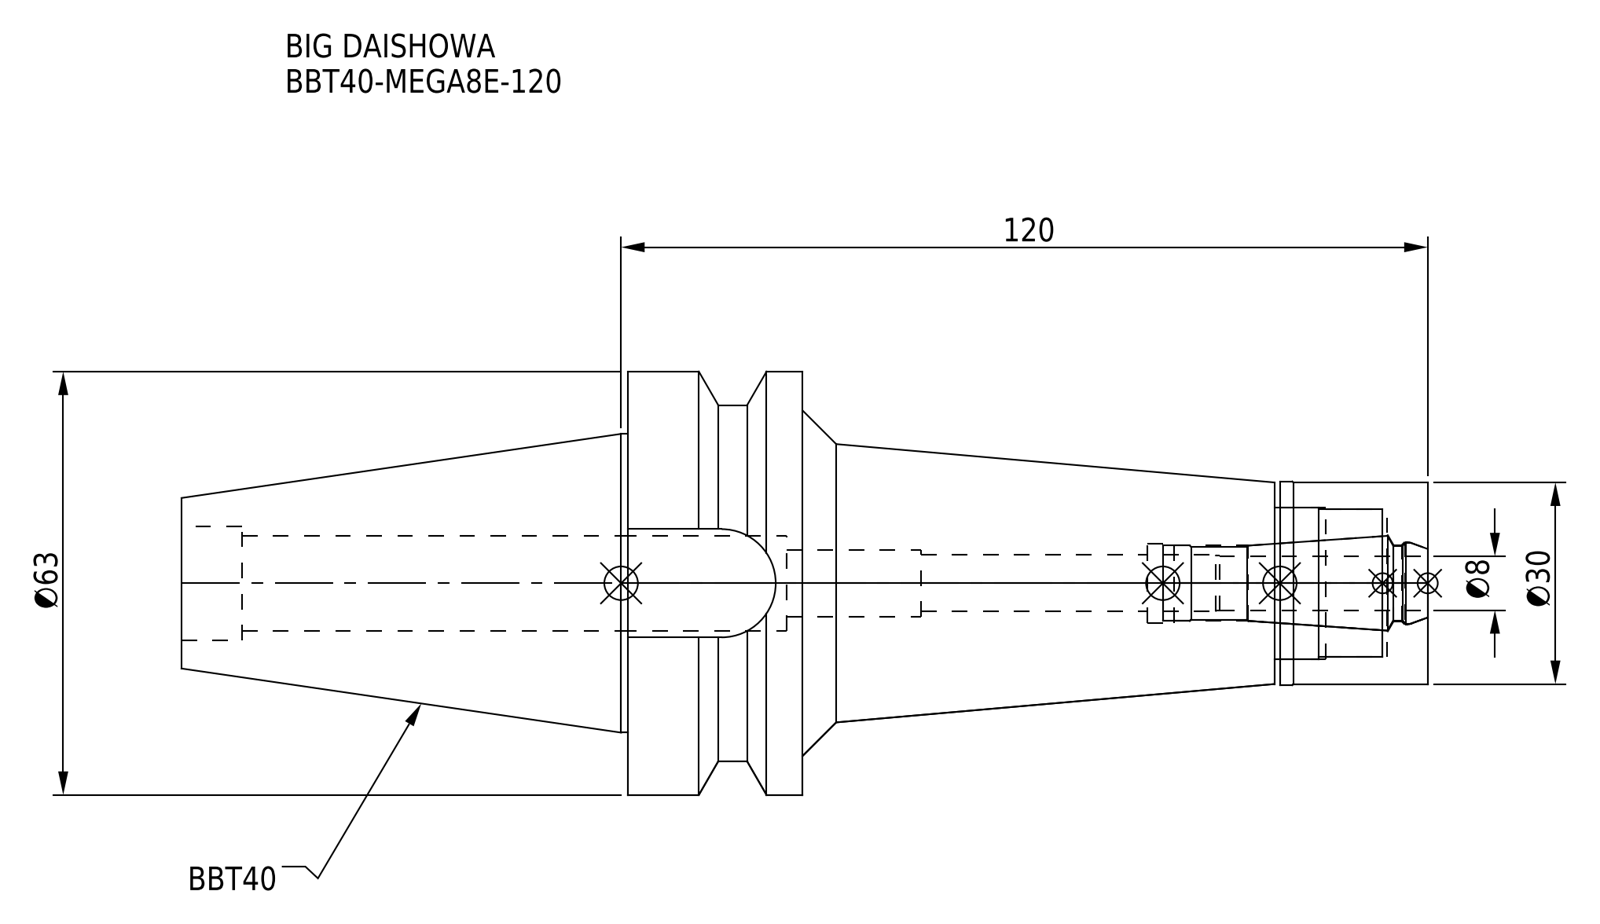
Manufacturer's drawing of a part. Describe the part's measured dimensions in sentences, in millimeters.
The part is named "DXF_TEMP_ASSY_ASM_4_ASM.stp; MEN8_1.stp; BBT40-MEGA8E-120-080-FreeParts; BBT40-MEGA8E-120-080.stp (+3 more)". Its 3-D file was written by "SolidWorks 2019 (CONFIG_CONTROL_DESIGN)". It is 2 solids with 81 faces: 21 planar, 40 cylindrical and 20 other. Overall it measures 185.4 by 63 by 63 millimeters. Its volume is 202 538 cubic millimeters and its surface area 38 383 square millimeters. Round holes: 1 of diameter 8.4, 1 of diameter 10, 1 of diameter 11.2, 1 of diameter 11.4, 1 of diameter 11.8, 1 of diameter 12.3, 1 of diameter 14.2, 1 of diameter 17, 1 of diameter 22, 1 of diameter 22.5. Round bosses or shafts: 1 of diameter 63, 1 of diameter 53, 1 of diameter 44.45, 1 of diameter 30.3, 1 of diameter 30. Partial cylindrical surfaces (rounded edges, fillets, slot ends): 1 of radius 8.05. The main face-to-face distances are 26, 93, 119, 16.1, 45, 22, 71, 97, 22.8, 0.8.
